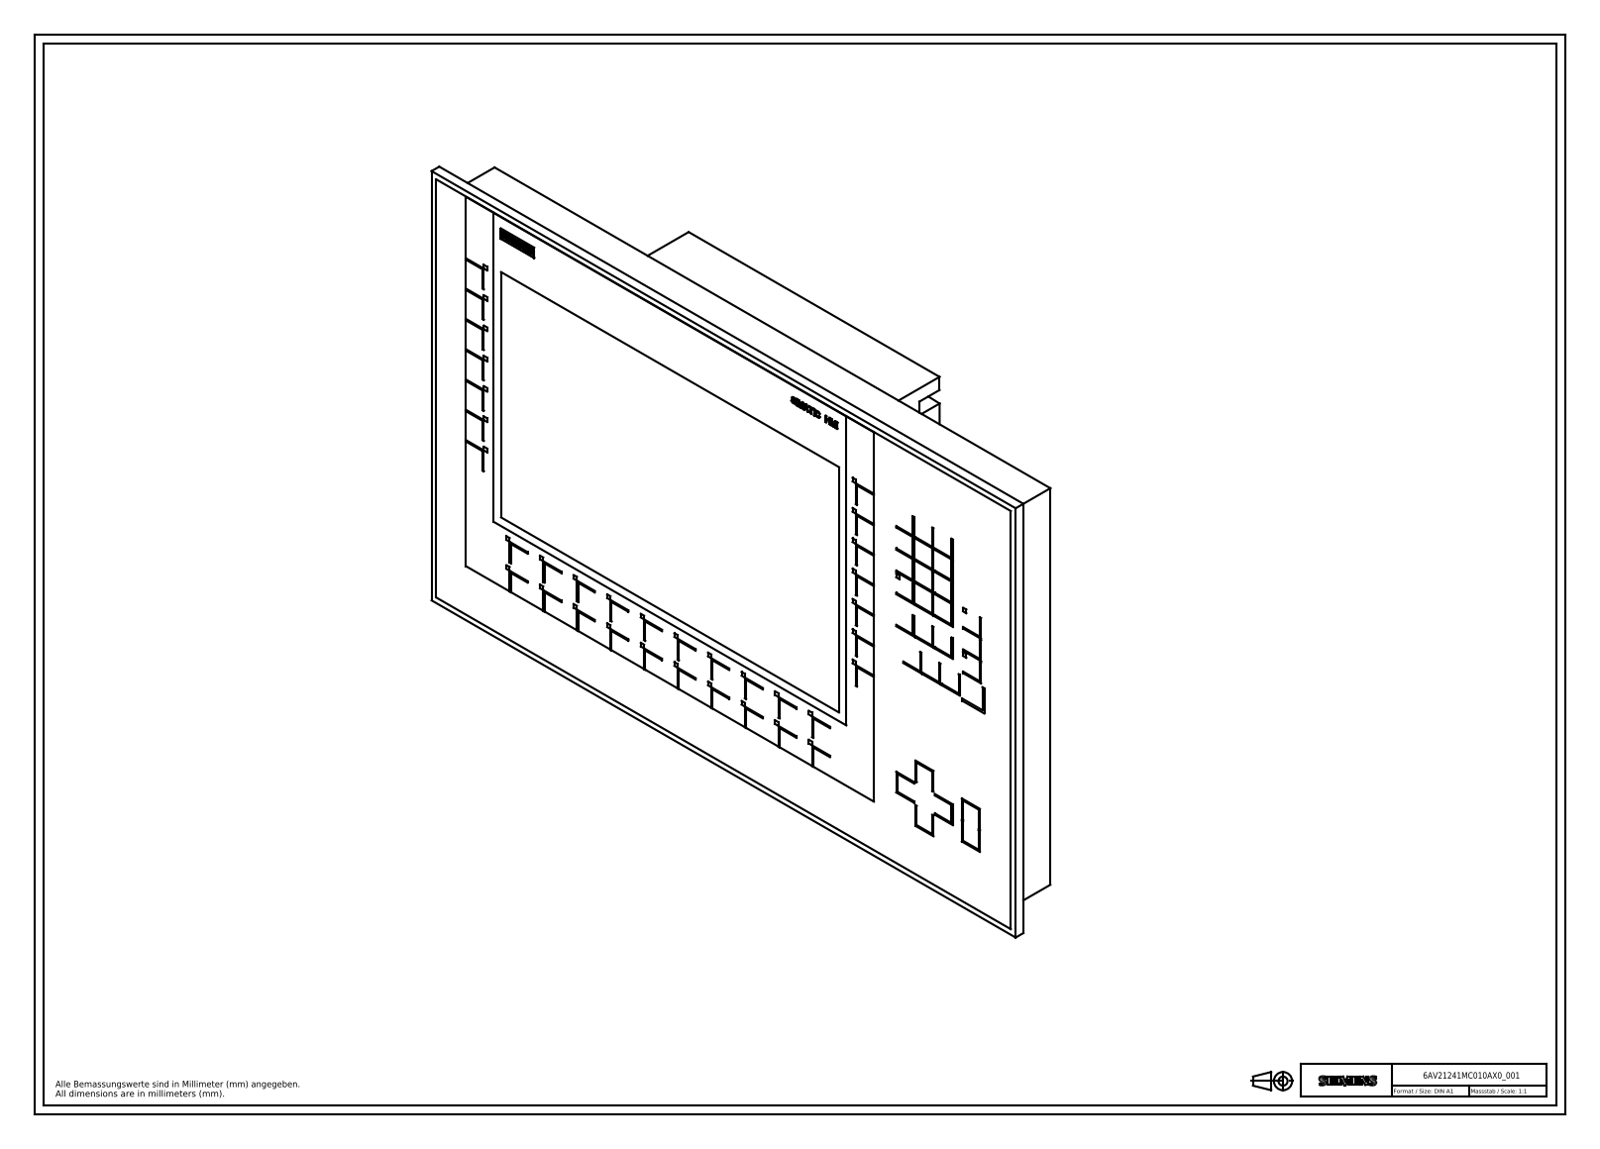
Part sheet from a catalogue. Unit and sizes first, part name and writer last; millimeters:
Units: millimetres
Overall size (bounding box): 454 × 289 × 70.6
Round holes (diameter × count): ⌀0.9 ×9, ⌀2.4 ×2, ⌀3.4 ×2, ⌀3.8 ×2, ⌀8.5 ×2
Round bosses / shafts (diameter × count): ⌀5.5 ×11, ⌀7 ×6, ⌀3 ×2, ⌀0.96 ×2, ⌀0.8 ×2, ⌀8 ×1
Partial cylindrical surfaces — rounded edges, fillets, slot ends (radius × count): R0.2 ×137, R0.1 ×49, R0.3 ×24, R0.8 ×24, R0.74 ×16, R0.11 ×7, R0.14 ×7, R0.85 ×6
Main face-to-face distances: 37.75, 36.73, 1.02, 70.25, 32.5, 69.23, 32, 70.2, 37.7, 0.97
Hole centre spacings: 3.07, 2.76, 4.96, 5.52, 7.42, 8.28, 7.15, 8.44
Volume: 4 560 000 mm³ · Surface area: 436 762 mm²
Bodies: 362 solids, 3841 faces (3201 planar, 357 cylindrical, 283 other)
Part name (STEP PRODUCT): A5E30321192A_001; A5E30292377A_001; A5E30292375A_001; A5E30292351A_001 (+1 more)
STEP written by: SIEMENS UGS NX 6.0 (AUTOMOTIVE_DESIGN)
